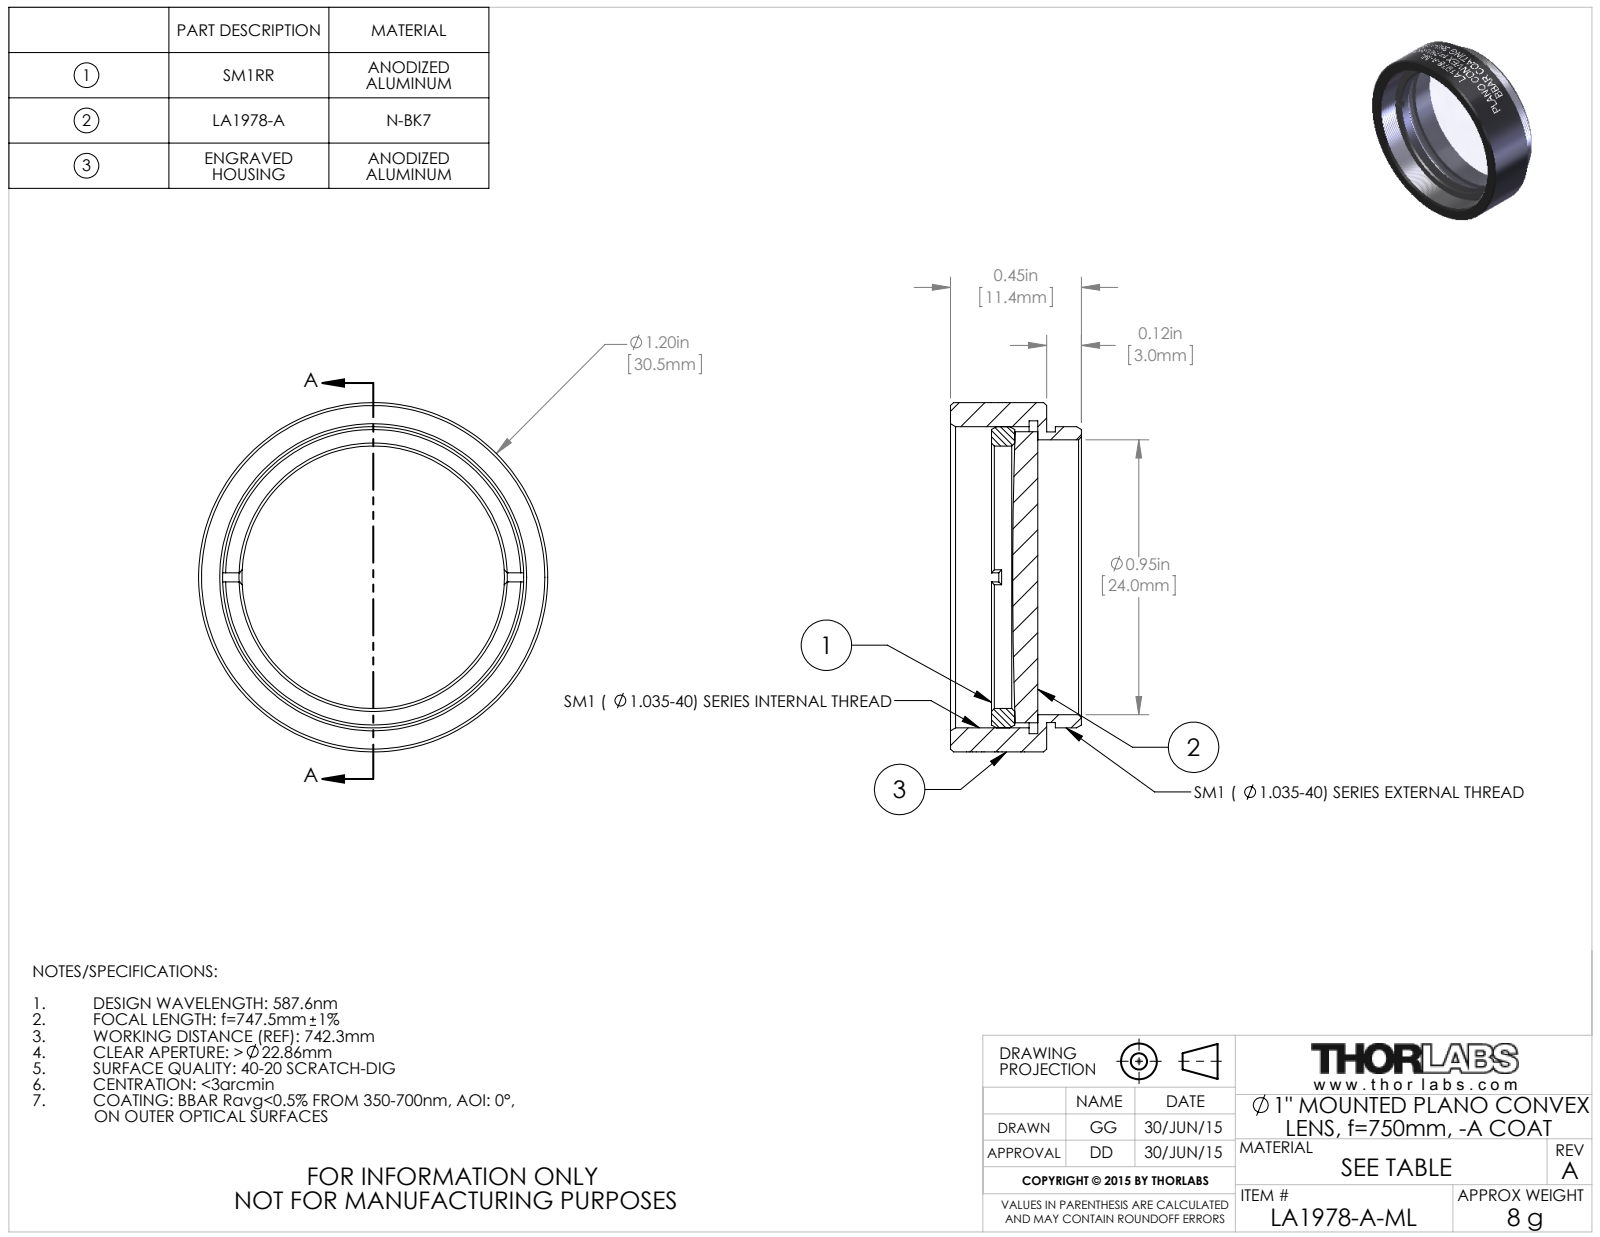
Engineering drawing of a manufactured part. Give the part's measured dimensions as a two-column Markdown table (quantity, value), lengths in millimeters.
| quantity | value |
| --- | --- |
| part name | TTN039657-E0W |
| STEP written by | SolidWorks 2014 (CONFIG_CONTROL_DESIGN) |
| units | millimeters |
| bodies | 3 solids, 153 faces (20 planar, 109 cylindrical, 24 other) |
| overall size | 30.5 × 30.5 × 11.4 |
| volume | 3 150 mm³ |
| surface area | 4 312 mm² |
| round holes (diameter × count) | 22.9 × 1, 24 × 1, 27.3 × 1 |
| round bosses / shafts (diameter × count) | 30.5 × 1, 26.3 × 1, 25.4 × 1, 25.4 × 1 |
| main face-to-face distances | 0.8, 2, 0.8, 8.4, 7.6, 7.6, 2.8, 2, 5.6, 4.8 |
